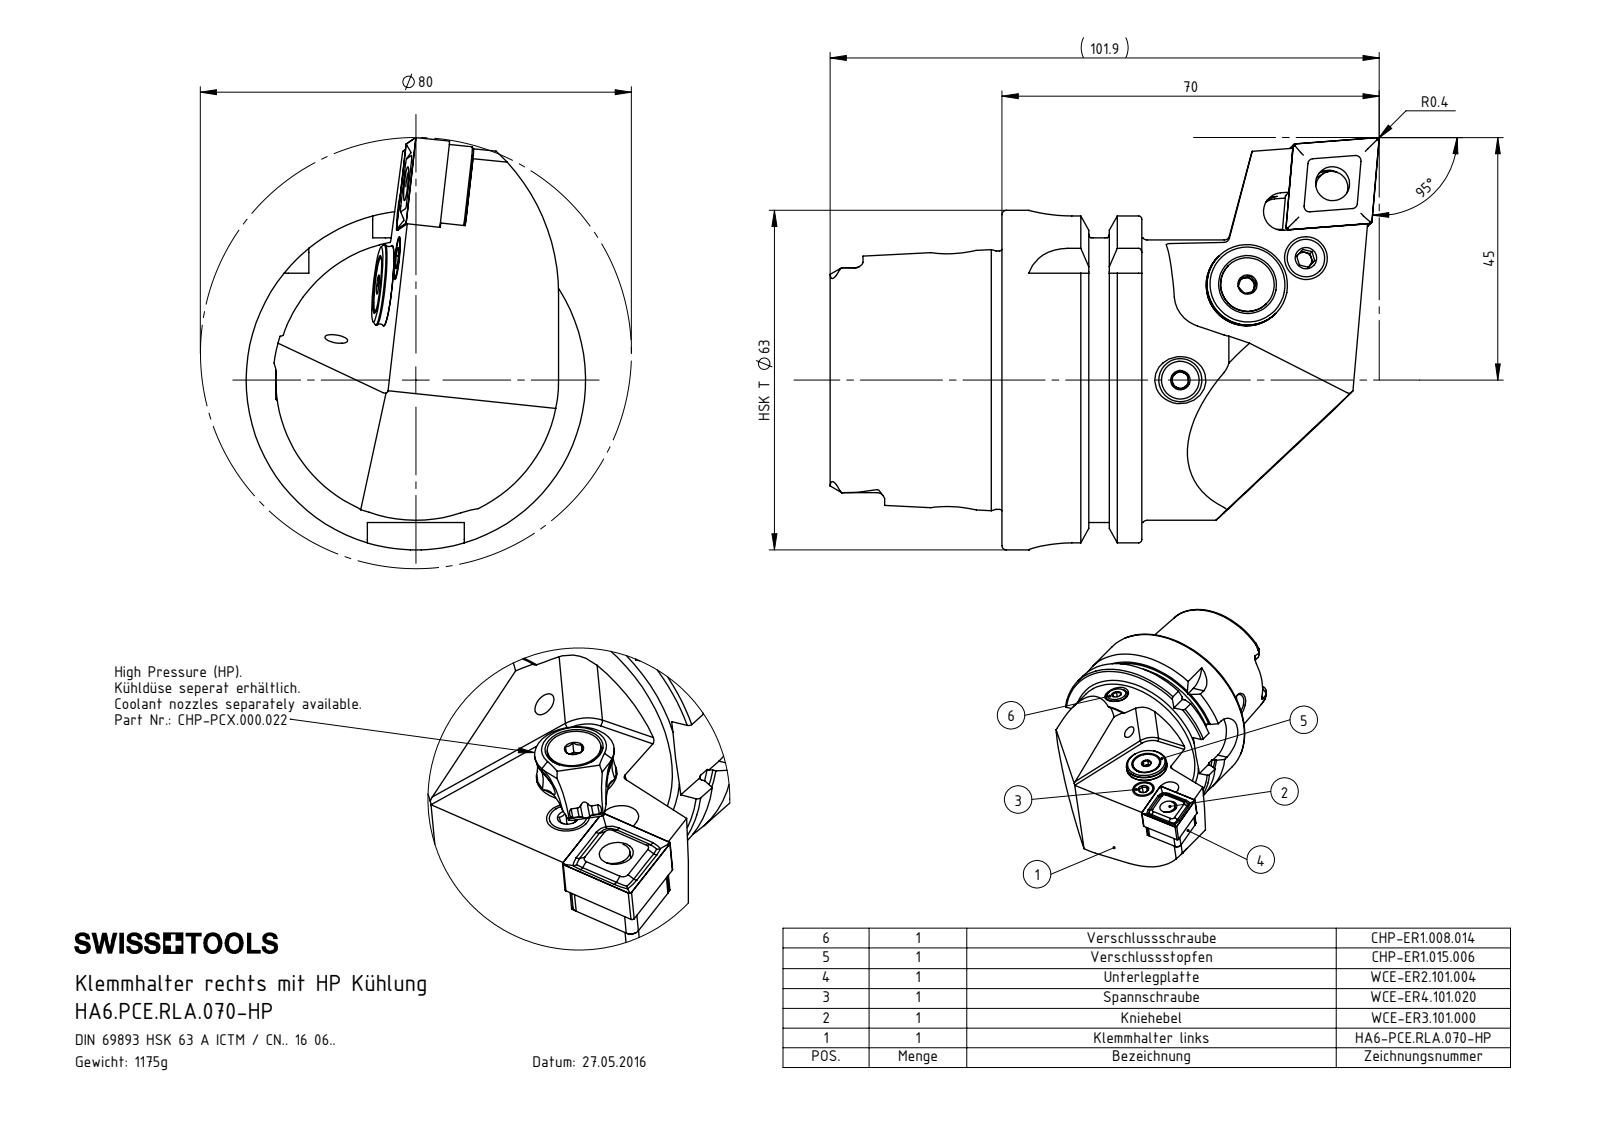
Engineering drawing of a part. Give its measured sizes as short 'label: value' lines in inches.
name: CHP-ER1.015.006; CNMG160604; CHP-ER1.015.006_A; WCE-ER2.101.004_A (+8 more)
written by: SolidWorks 2017 (AUTOMOTIVE_DESIGN)
unit: in
bodies: 10 solids, 498 faces (159 planar, 137 cylindrical, 202 other)
size: 4.012 × 3.012 × 2.48
volume: 9.089 in³; area: 56.76 in²
holes: 3× ⌀0.165, 2× ⌀0.276, 2× ⌀0.331, 1× ⌀0.047, 1× ⌀0.079, 1× ⌀0.098, 1× ⌀0.118, 1× ⌀0.197, 1× ⌀0.205, 1× ⌀0.25, 1× ⌀0.295, 1× ⌀0.317
bosses: 2× ⌀0.315, 1× ⌀2.48, 1× ⌀2.163, 1× ⌀2.047, 1× ⌀1.887, 1× ⌀0.591, 1× ⌀0.528, 1× ⌀0.394
rounds: 6× R0.055, 4× R0.016, 4× R0.059, 4× R0.113, 4× R0.138, 4× R0.315, 2× R0.012, 2× R0.031
face distances: 1.022, 0.63, 0.392, 0.238, 1.256, 1.648, 2.278, 2.079, 0.858, 0.467
hole spacings: 0.177, 0.406, 0.834, 0.844, 0.985, 0.178, 0.484, 0.484
